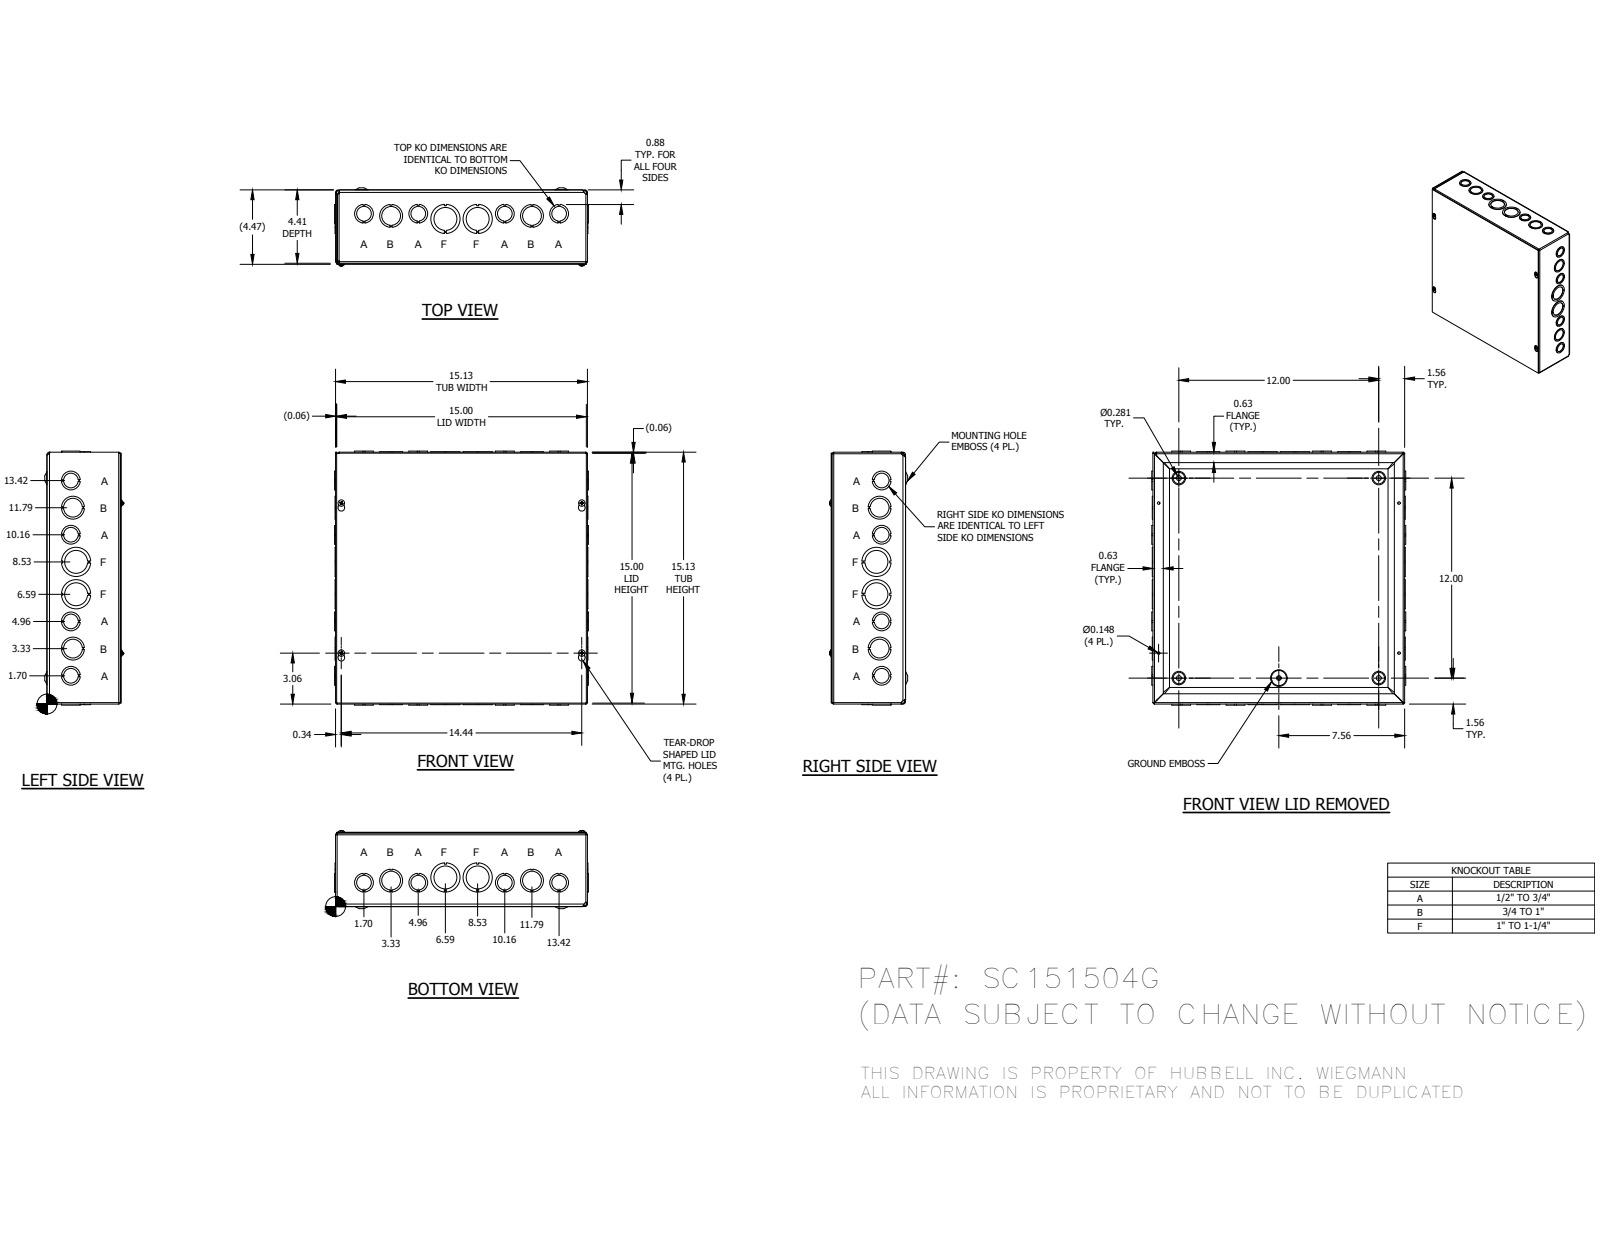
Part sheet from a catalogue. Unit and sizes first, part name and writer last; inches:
Units: inches
Overall size (bounding box): 15.249 × 15.249 × 4.693
Round holes (diameter × count): ⌀1.125 ×12, ⌀0.875 ×8, ⌀1.375 ×8, ⌀0.148 ×4, ⌀0.3 ×4, ⌀1.75 ×4, ⌀0.165 ×1
Round bosses / shafts (diameter × count): ⌀0.384 ×4, ⌀0.164 ×4, ⌀0.228 ×1
Partial cylindrical surfaces — rounded edges, fillets, slot ends (radius × count): R0.031 ×8, R0.093 ×8, R0.055 ×4, R0.062 ×4, R0.094 ×4, R0.11 ×4, R0.117 ×4, R0.124 ×4
Main face-to-face distances: 0.062, 4.343, 4.405, 0.063, 4.406, 4.468, 0.062, 15.125, 15.063, 15.063
Hole centre spacings: 1.635, 1.659, 1.933, 3.265, 3.584, 5.204, 6.831, 8.46
Bodies: 38 solids, 1254 faces (838 planar, 265 cylindrical, 151 other)
Part name (STEP PRODUCT): SC1515GBKP; SC151504GWRA; SC1515GLID; 34056 (+1 more)
STEP written by: Autodesk Inventor 2014 (AUTOMOTIVE_DESIGN)
